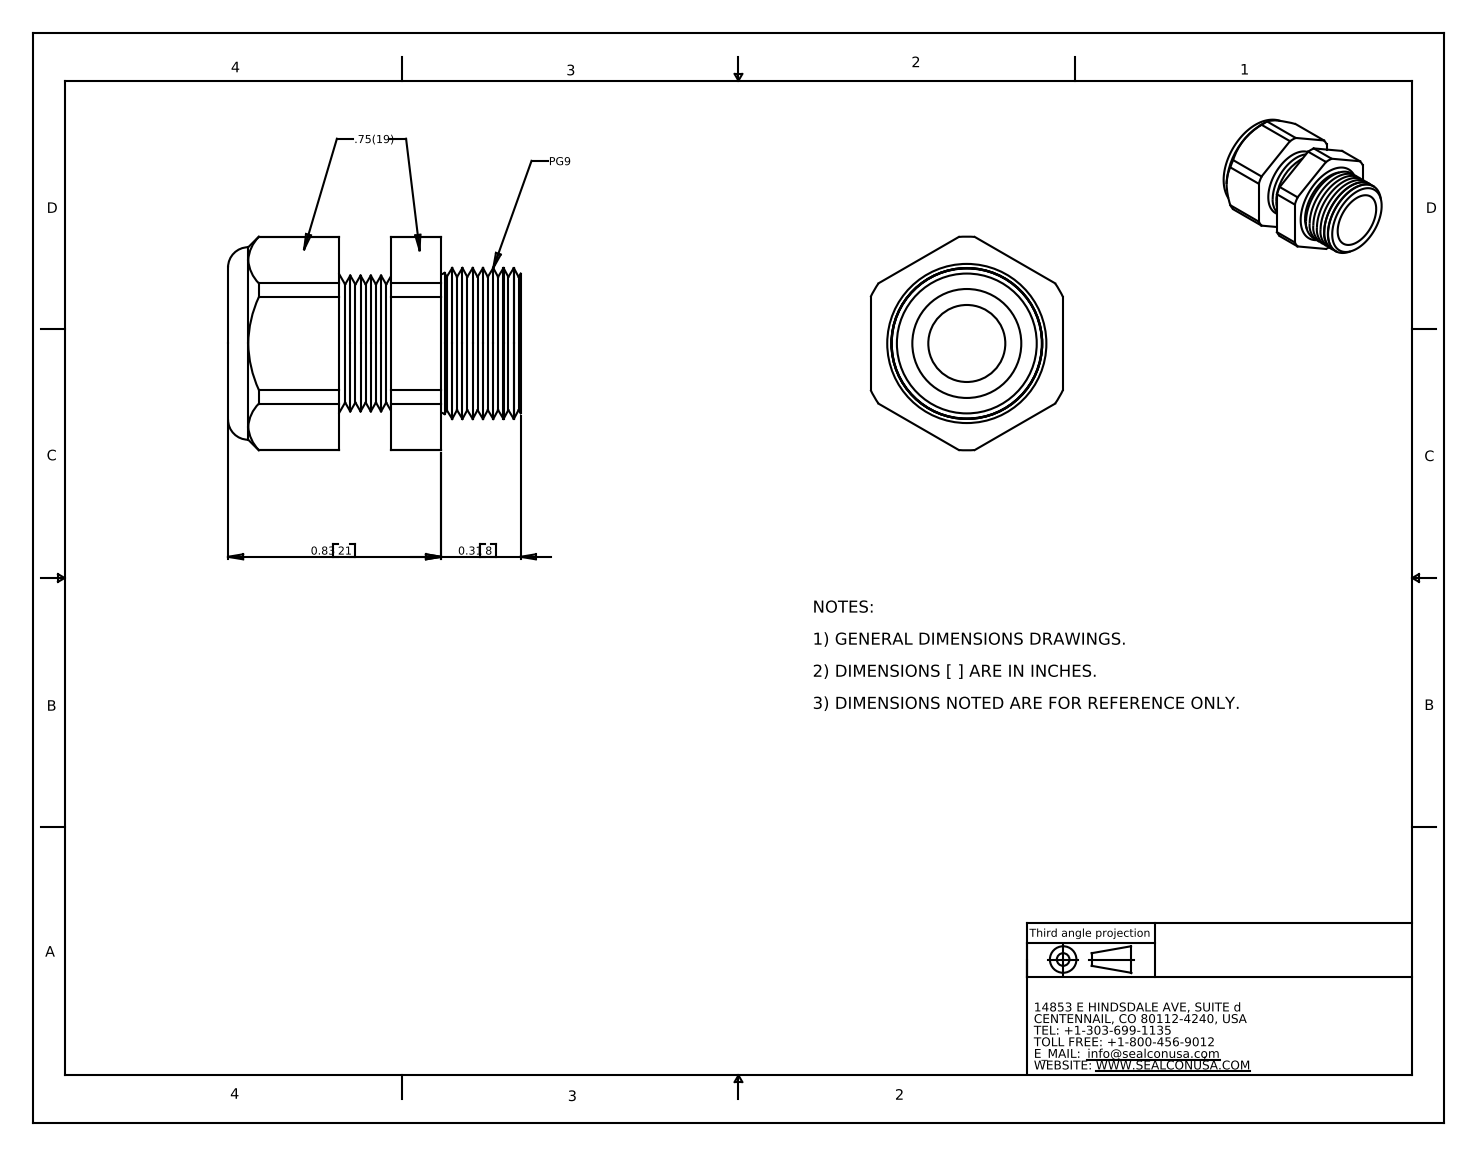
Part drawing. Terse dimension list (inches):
name: CD09BA-GY
written by: SolidWorks 2007 (CONFIG_CONTROL_DESIGN)
unit: in
bodies: 2 solids, 114 faces (20 planar, 22 cylindrical, 72 other)
size: 1.14 × 0.833 × 0.75
volume: 0.309 in³; area: 7.115 in²
holes: 1× ⌀0.3, 1× ⌀0.48, 1× ⌀0.54
rounds: 1× R0.416
face distances: 0.75, 0.2, 0.75, 0.397, 0.197, 0.403, 0.603, 0.8, 0.03, 0.433
